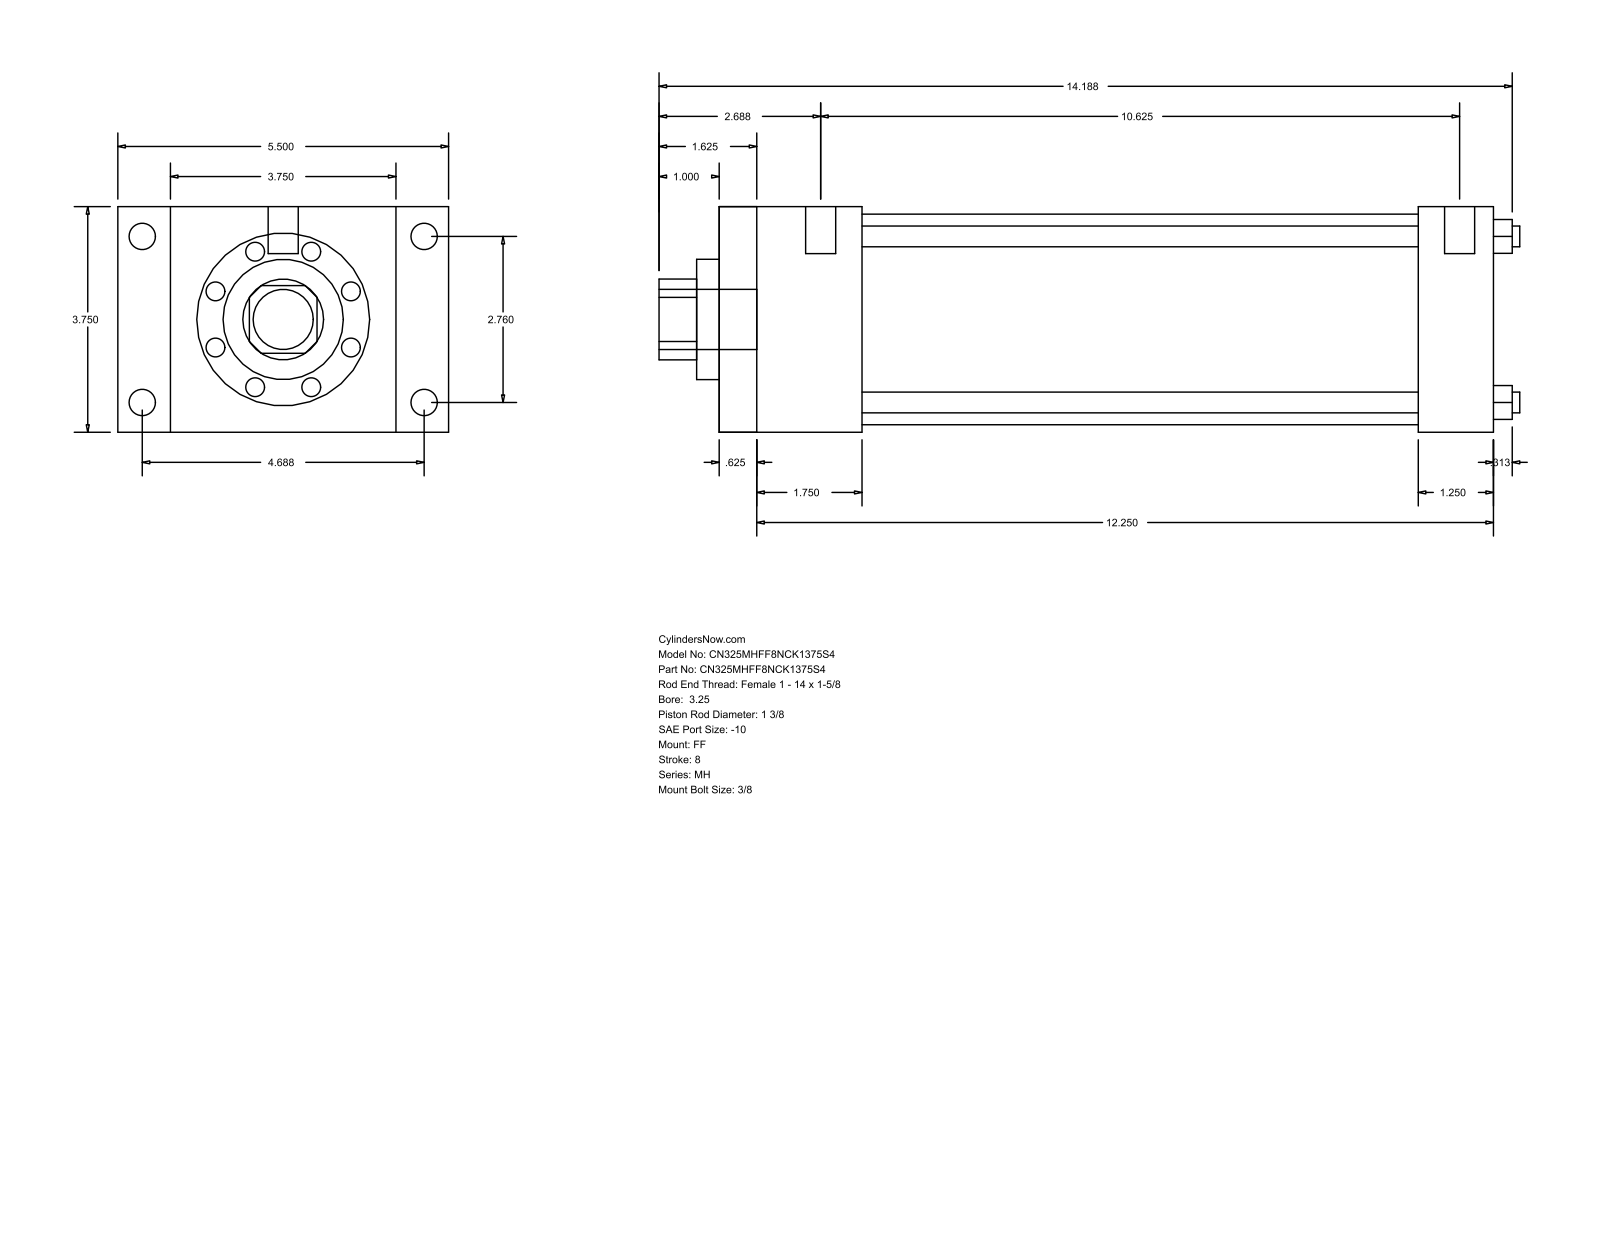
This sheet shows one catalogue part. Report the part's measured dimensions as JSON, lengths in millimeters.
{"part_name": "MH_FF__0325_1.375", "step_written_by": "GSSL Pune (CONFIG_CONTROL_DESIGN)", "units": "millimeters", "bodies": {"solids": 0, "faces": 92, "planar": 64, "cylindrical": 28, "other": 0}, "overall_size": [363.54, 139.7, 95.25], "round_holes": [[8.76, 4], [34.92, 1], [50.8, 1], [88.9, 1]], "round_bosses_or_shafts": [[11.13, 4], [5.56, 4], [12.7, 2], [25.4, 1]], "partial_cylinders_radius": [[17.06, 1]], "face_to_face_distances": [95.24, 327.03, 15.87, 311.16, 22.23, 117.47, 295.28, 279.41, 31.75, 60.32], "hole_center_spacings": [49.57, 70.1, 99.14]}
